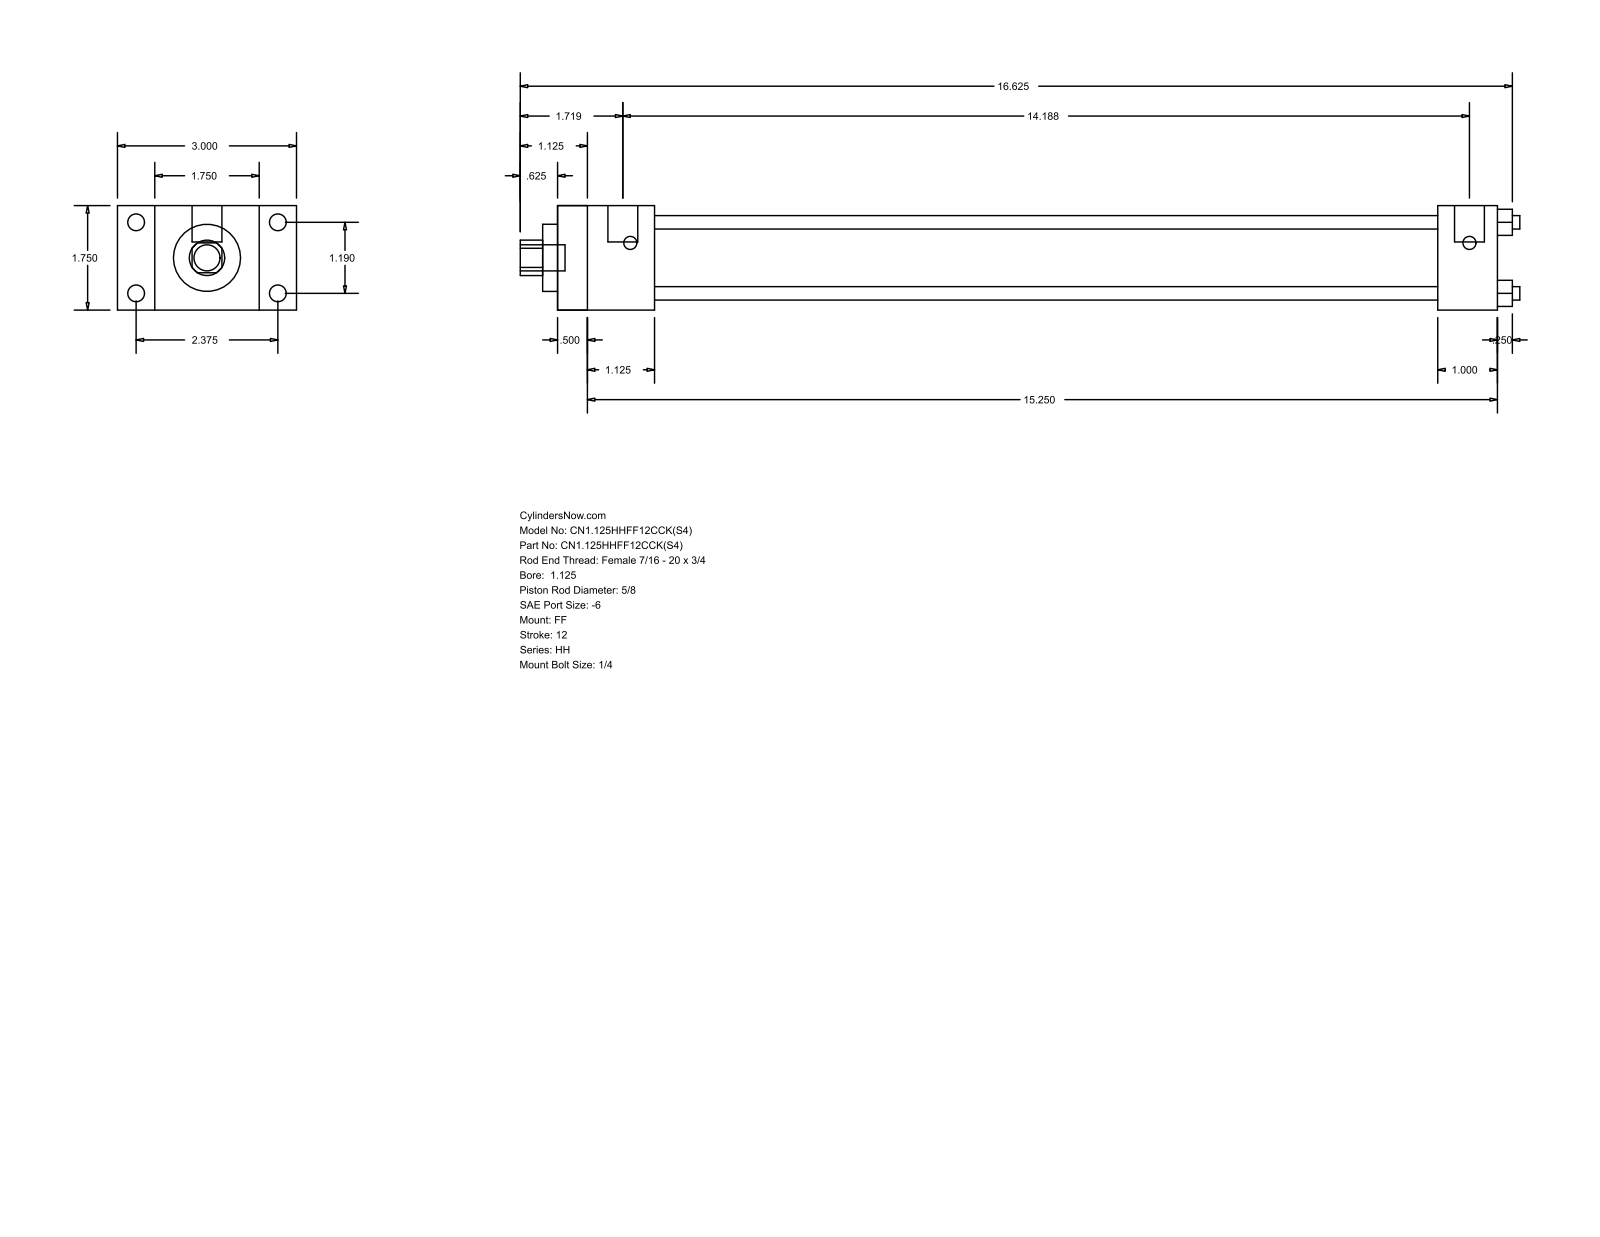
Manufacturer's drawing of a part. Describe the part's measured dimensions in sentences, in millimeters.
The part is named "HH_FF__0112_0.625". Its 3-D file was written by "GSSL Pune (CONFIG_CONTROL_DESIGN)". It is 0 solids with 92 faces: 64 planar, 28 cylindrical and 0 other. Overall it measures 425.45 by 76.2 by 44.45 millimeters. Round holes: 4 of diameter 5.71, 1 of diameter 15.88, 1 of diameter 28.57, 1 of diameter 34.92. Round bosses or shafts: 4 of diameter 7.14, 4 of diameter 5.56, 2 of diameter 12.7, 1 of diameter 11.11. Partial cylindrical surfaces (rounded edges, fillets, slot ends): 1 of radius 7.54. The main face-to-face distances are 44.46, 400.05, 12.69, 387.36, 15.87, 60.33, 28.58, 41.27, 374.64, 361.95. The hole center spacings are 21.37, 30.22, 42.74.
